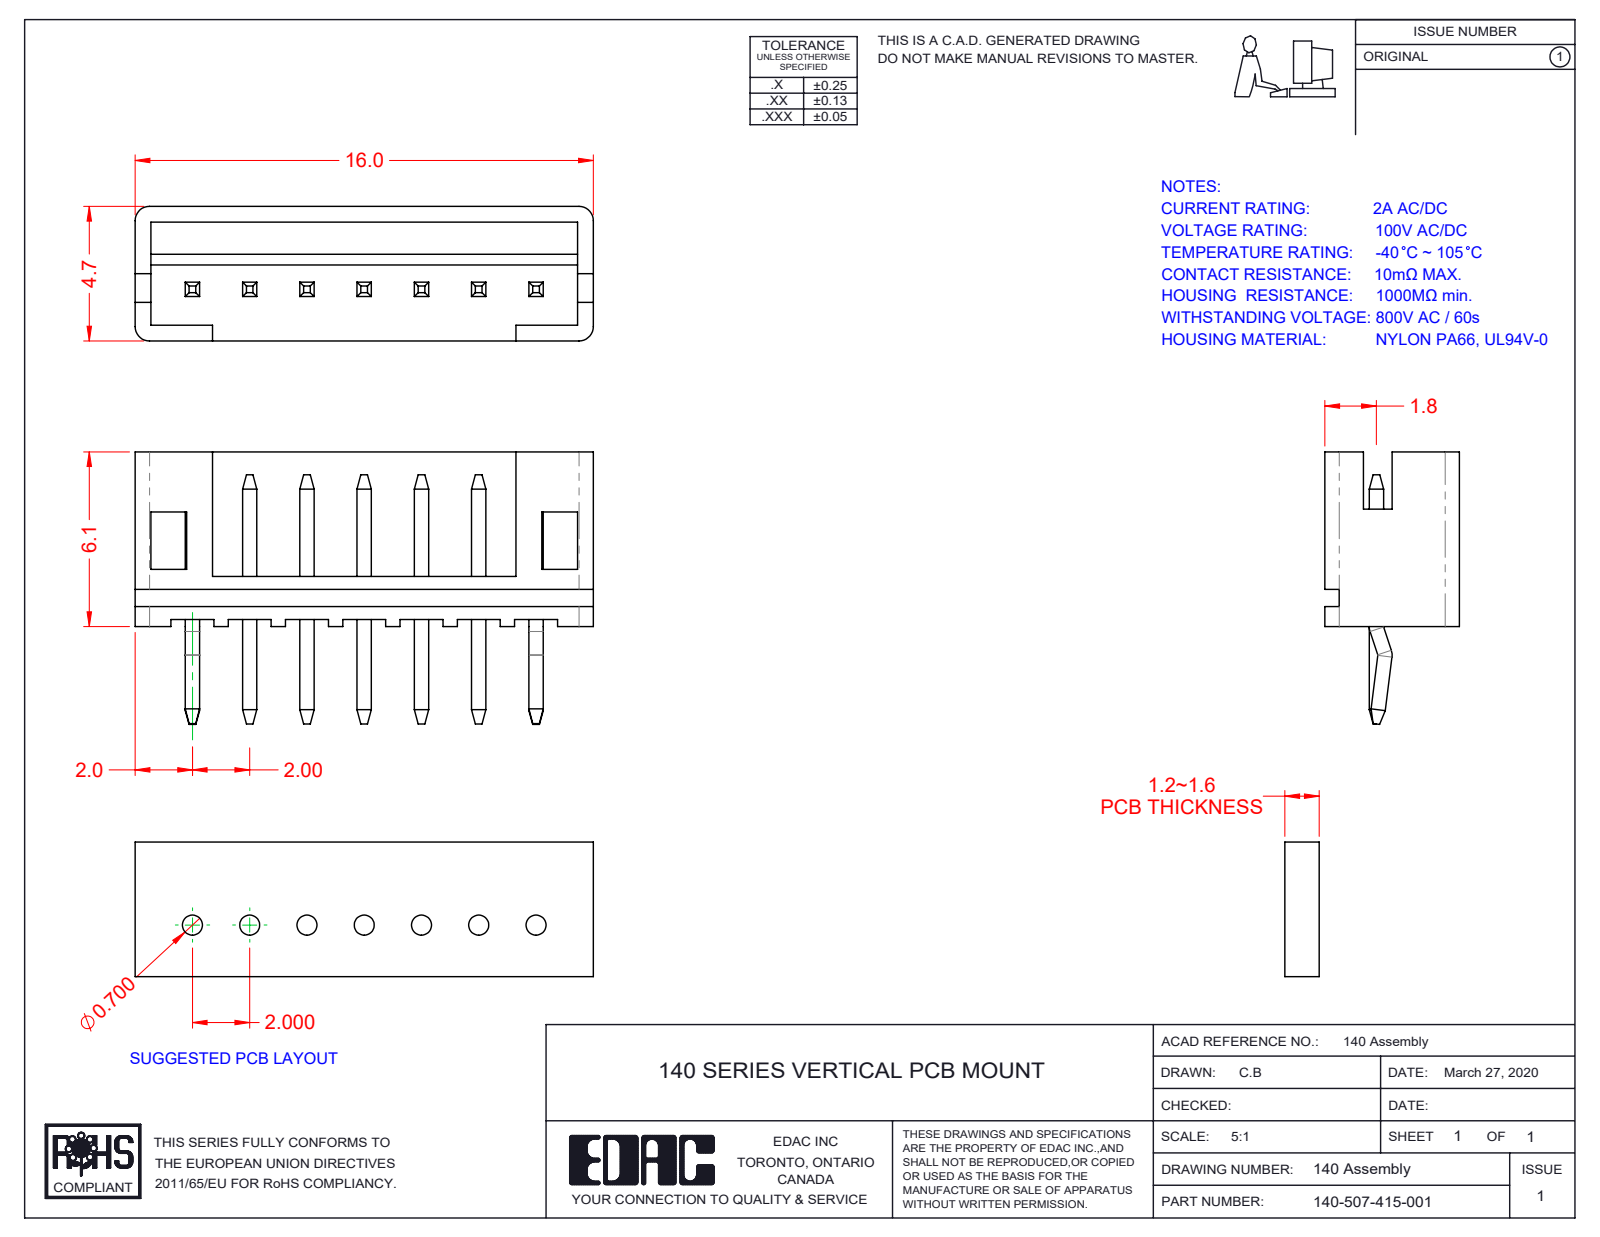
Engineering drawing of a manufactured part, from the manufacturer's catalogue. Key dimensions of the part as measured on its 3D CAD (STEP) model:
Part name (STEP PRODUCT): V Housing_507; V Contact_Kink; V Contact_Str; 140-507-415-001
STEP written by: SolidWorks 2016 (CONFIG_CONTROL_DESIGN)
Units: millimetres
Bodies: 8 solids, 224 faces (206 planar, 16 cylindrical, 2 other)
Overall size (bounding box): 16 × 9.52 × 4.7
Volume: 176 mm³ · Surface area: 645 mm²
Partial cylindrical surfaces — rounded edges, fillets, slot ends (radius × count): R0.5 ×4, R0.55 ×1
Main face-to-face distances: 0.55, 1.5, 0.5, 2, 4, 4.15, 1.55, 6, 1.75, 2.1
